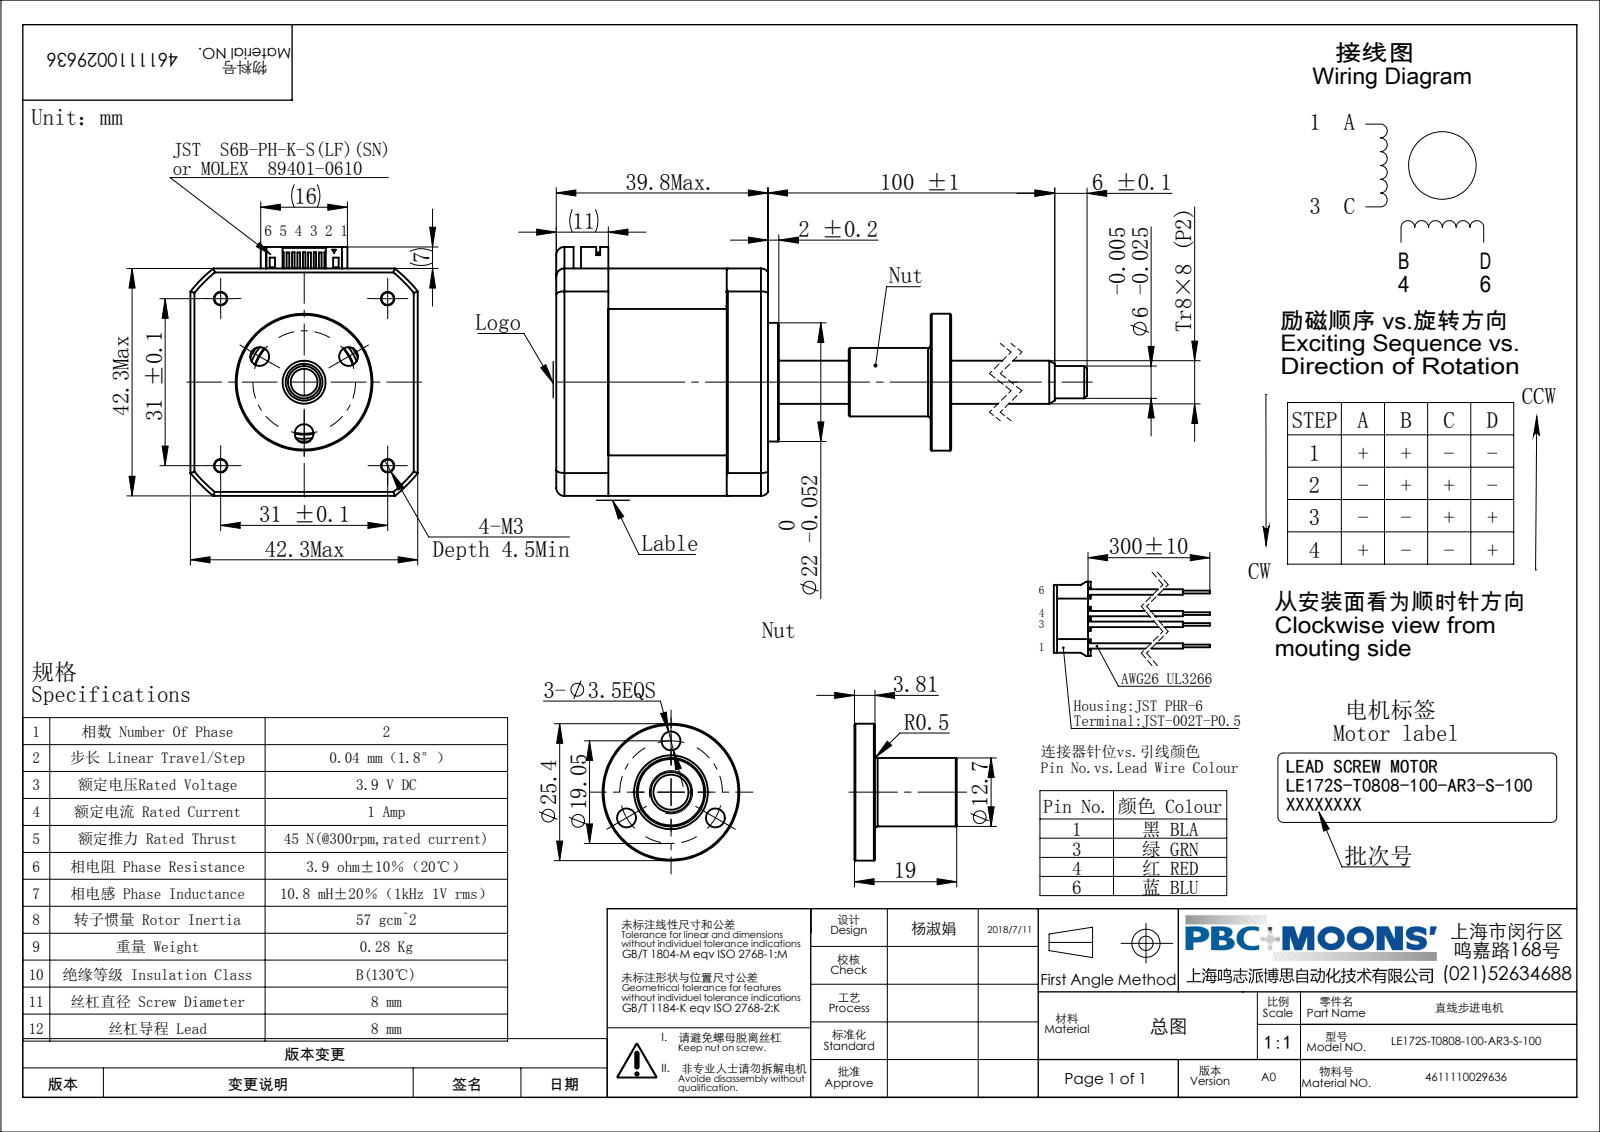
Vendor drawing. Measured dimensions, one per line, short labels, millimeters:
name: LE172S-T0808-100-AR3-S-100
written by: SolidWorks 2014 (CONFIG_CONTROL_DESIGN)
unit: mm
bodies: 0 solids, 318 faces (164 planar, 80 cylindrical, 74 other)
size: 145.3 × 46.2 × 42.2
holes: 4× ⌀2.5, 4× ⌀6, 3× ⌀3.5, 2× ⌀1.5, 2× ⌀2.05, 1× ⌀4.9, 1× ⌀10, 1× ⌀13, 1× ⌀19.46
bosses: 1× ⌀25.4, 1× ⌀22, 1× ⌀12.7, 1× ⌀9, 1× ⌀8, 1× ⌀6
rounds: 11× R1.5, 2× R2.5, 1× R25.1, 1× R27
face distances: 42.2, 9.65, 39.3, 29.65, 34, 2, 73.3, 63.65, 36, 69.49
hole spacings: 16.61, 21.92, 29.44, 31, 9.52, 16.5, 4.93, 8
